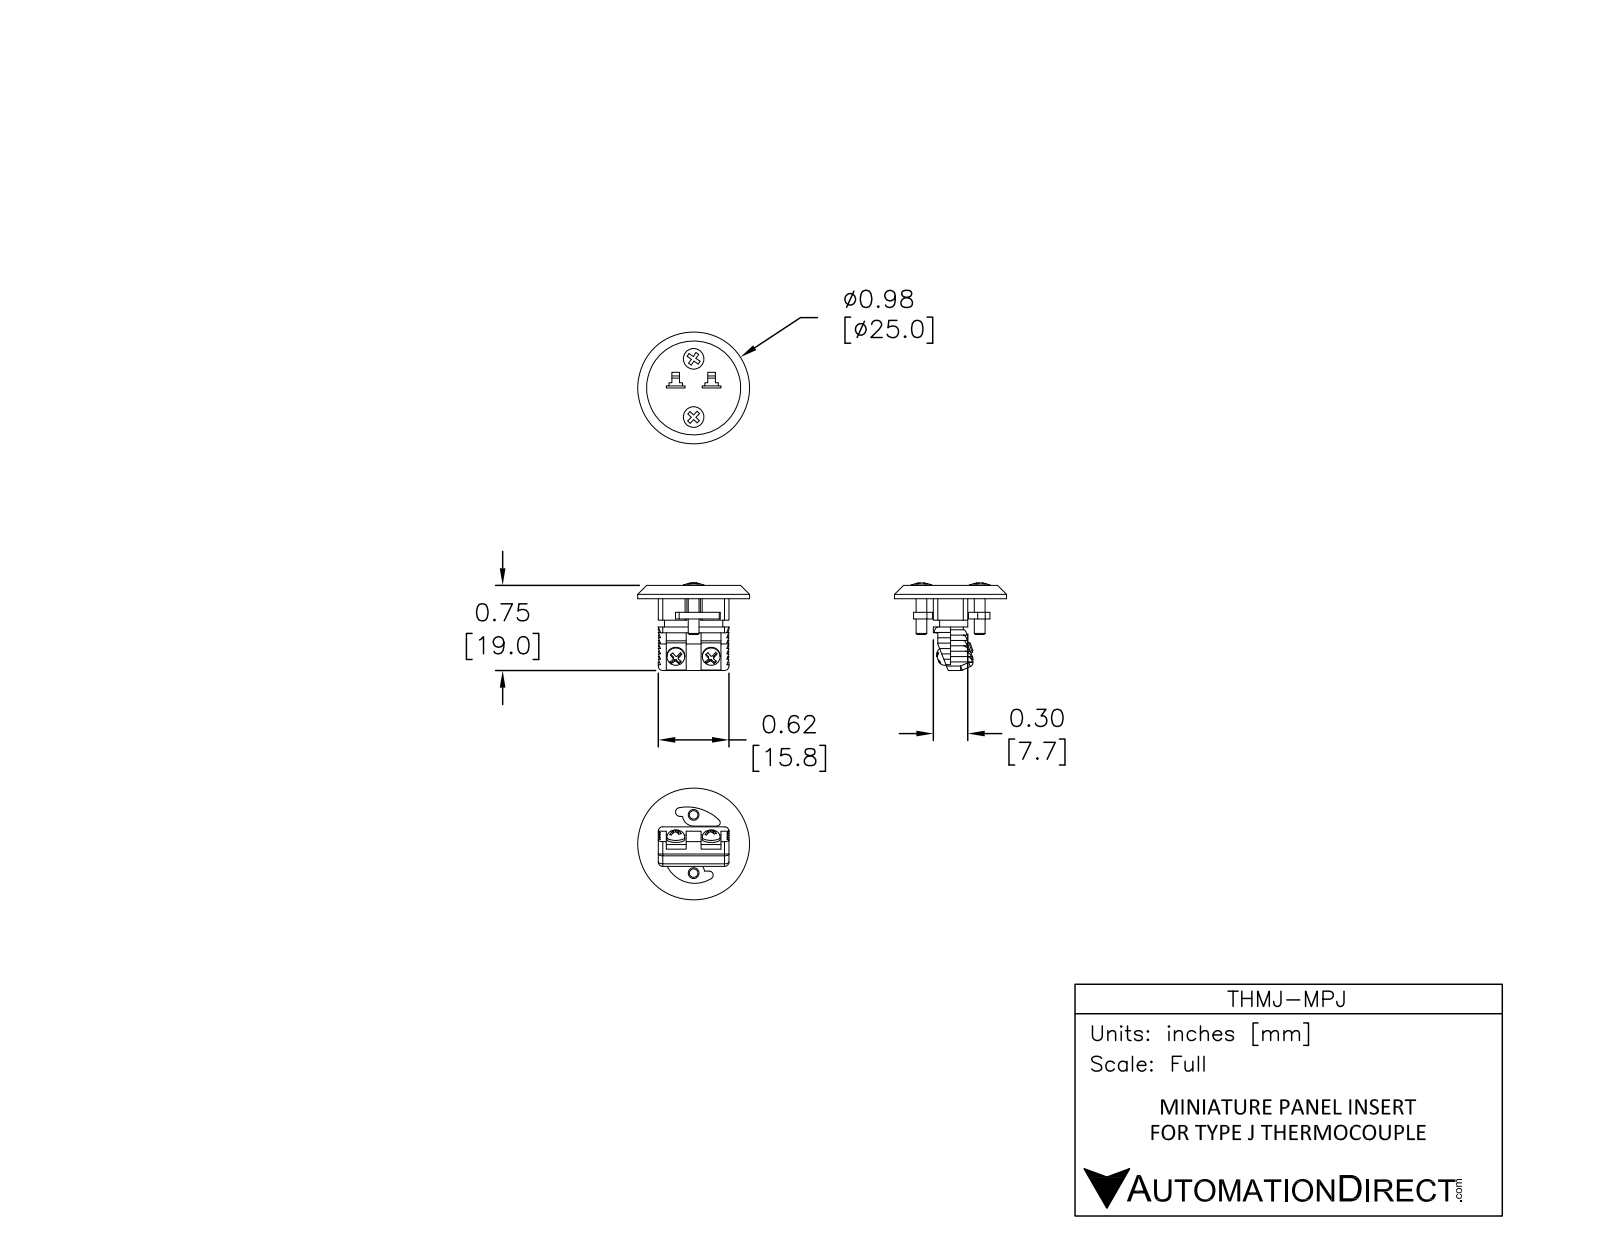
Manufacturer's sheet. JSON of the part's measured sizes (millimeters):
{"part_name": "THMJ-MPJ", "step_written_by": "SolidWorks 2017 (AUTOMOTIVE_DESIGN)", "units": "millimeters", "bodies": {"solids": 1, "faces": 357, "planar": 265, "cylindrical": 66, "other": 26}, "overall_size": [25, 25, 19.57], "volume_mm3": 2912, "surface_area_mm2": 2670, "round_bosses_or_shafts": [[4.6, 2], [4, 2], [2.4, 2], [2.3, 2], [25, 1]], "partial_cylinders_radius": [[1, 16], [0.25, 8], [0.75, 2], [2.5, 2], [0.5, 1], [0.91, 1], [0.98, 1], [6.93, 1]], "face_to_face_distances": [2.97, 5, 1.5, 7.67, 6, 1.79, 0.46, 7.77, 0.69, 2.67]}
